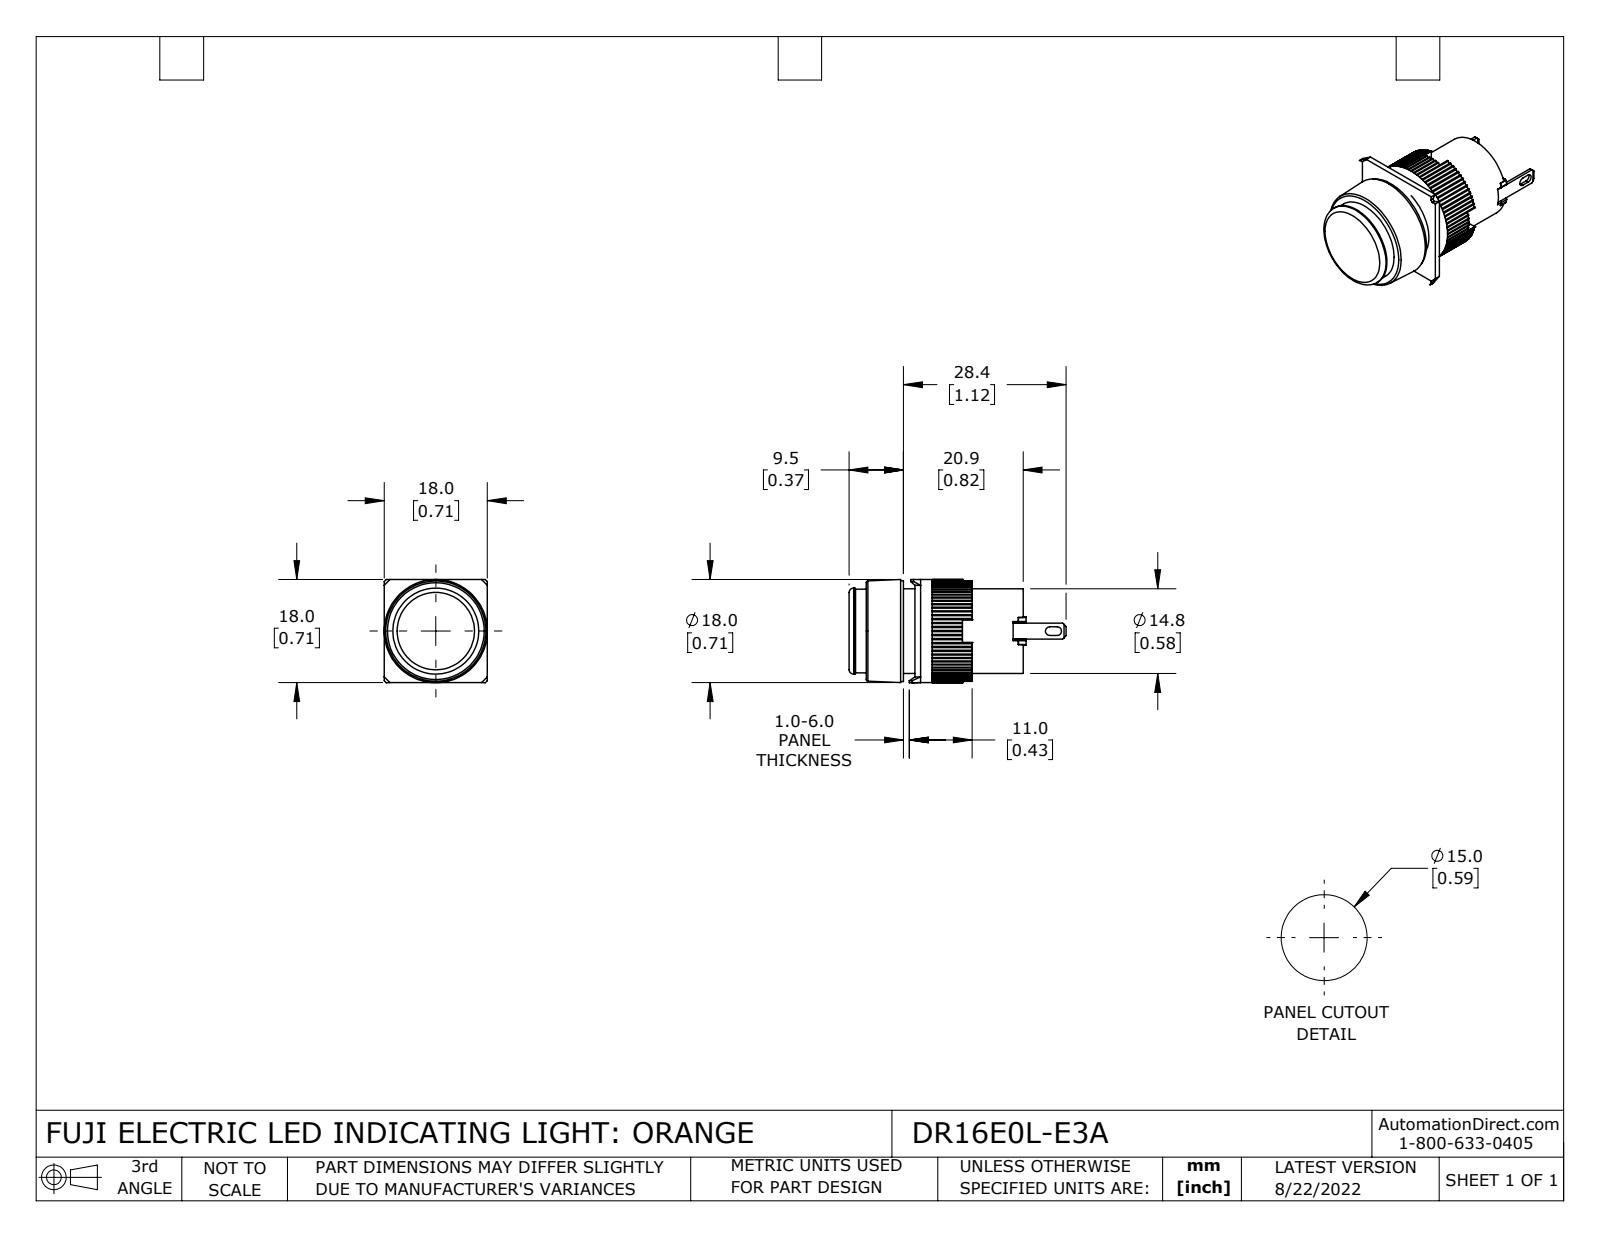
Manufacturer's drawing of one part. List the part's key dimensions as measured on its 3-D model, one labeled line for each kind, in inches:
Part name (STEP PRODUCT): DR16E0L-E3A
STEP written by: SolidWorks 2021 (CONFIG_CONTROL_DESIGN)
Units: inches
Bodies: 10 solids, 476 faces (295 planar, 171 cylindrical, 10 other)
Overall size (bounding box): 1.492 × 0.709 × 0.709
Volume: 0.349 in³ · Surface area: 7.224 in²
Round holes (diameter × count): ⌀0.543 ×1, ⌀0.575 ×1, ⌀0.583 ×1
Round bosses / shafts (diameter × count): ⌀0.709 ×1, ⌀0.693 ×1, ⌀0.591 ×1
Partial cylindrical surfaces — rounded edges, fillets, slot ends (radius × count): R0.01 ×80, R0.008 ×8, R0.03 ×2
Main face-to-face distances: 0.138, 0.35, 0.705, 0.354, 0.492, 0.213, 0.453, 0.843, 0.098, 0.039
